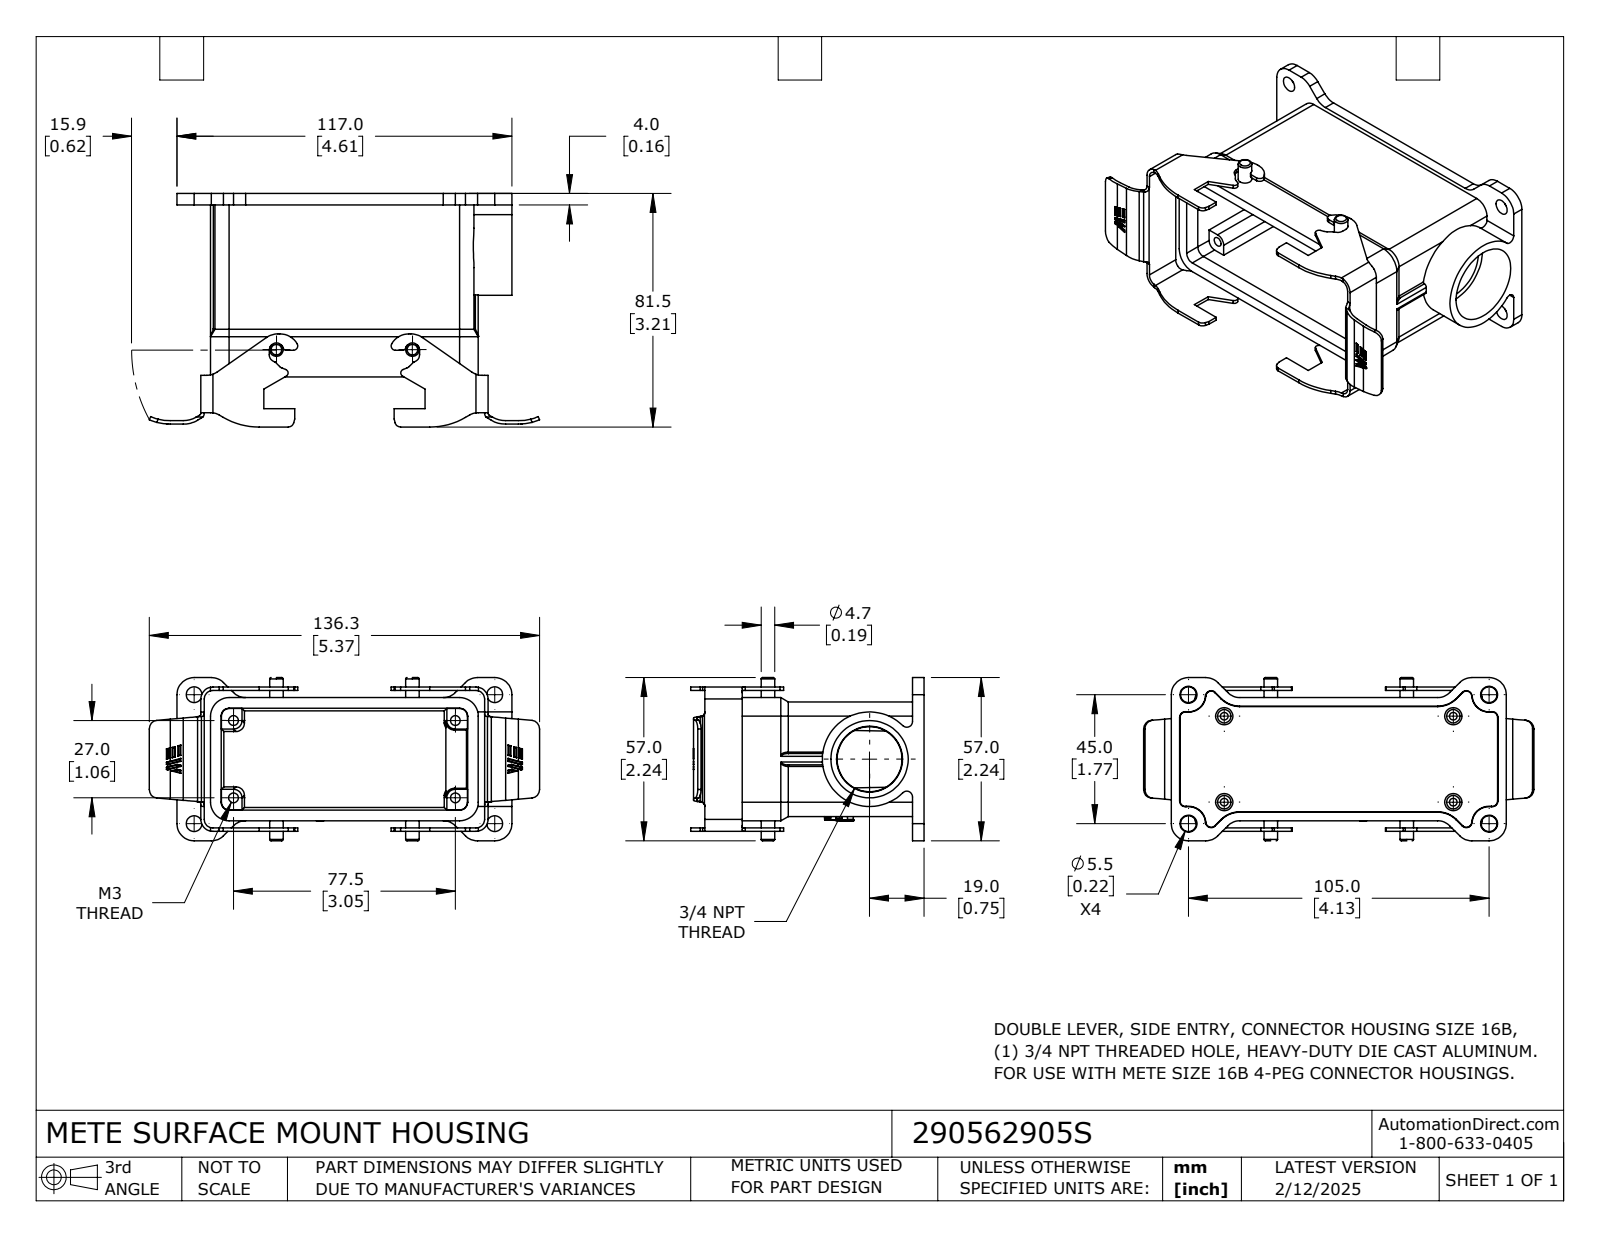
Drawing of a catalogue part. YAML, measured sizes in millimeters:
part_name: "290562905S"
step_written_by: "SolidWorks 2024 (CONFIG_CONTROL_DESIGN)"
units: millimeters
bodies: {solids: 1, faces: 510, planar: 211, cylindrical: 229, other: 70}
overall_size: [136.3, 81.5, 57]
volume: 77790
surface_area: 56660
round_holes:
  - {diameter: 3.4, count: 4}
  - {diameter: 27, count: 1}
round_bosses_or_shafts:
  - {diameter: 4.7, count: 2}
partial_cylinders:
  - {radius: 0.2, count: 60}
  - {radius: 6, count: 16}
  - {radius: 3, count: 12}
  - {radius: 0.5, count: 10}
  - {radius: 1, count: 6}
  - {radius: 1.5, count: 6}
  - {radius: 2, count: 6}
  - {radius: 2.5, count: 6}
face_to_face_distances: [2.5, 1.5, 3.7, 1.2, 4, 40, 41.5, 5.2, 45.5, 44]
hole_center_spacings: [27, 77.5, 82.1]
